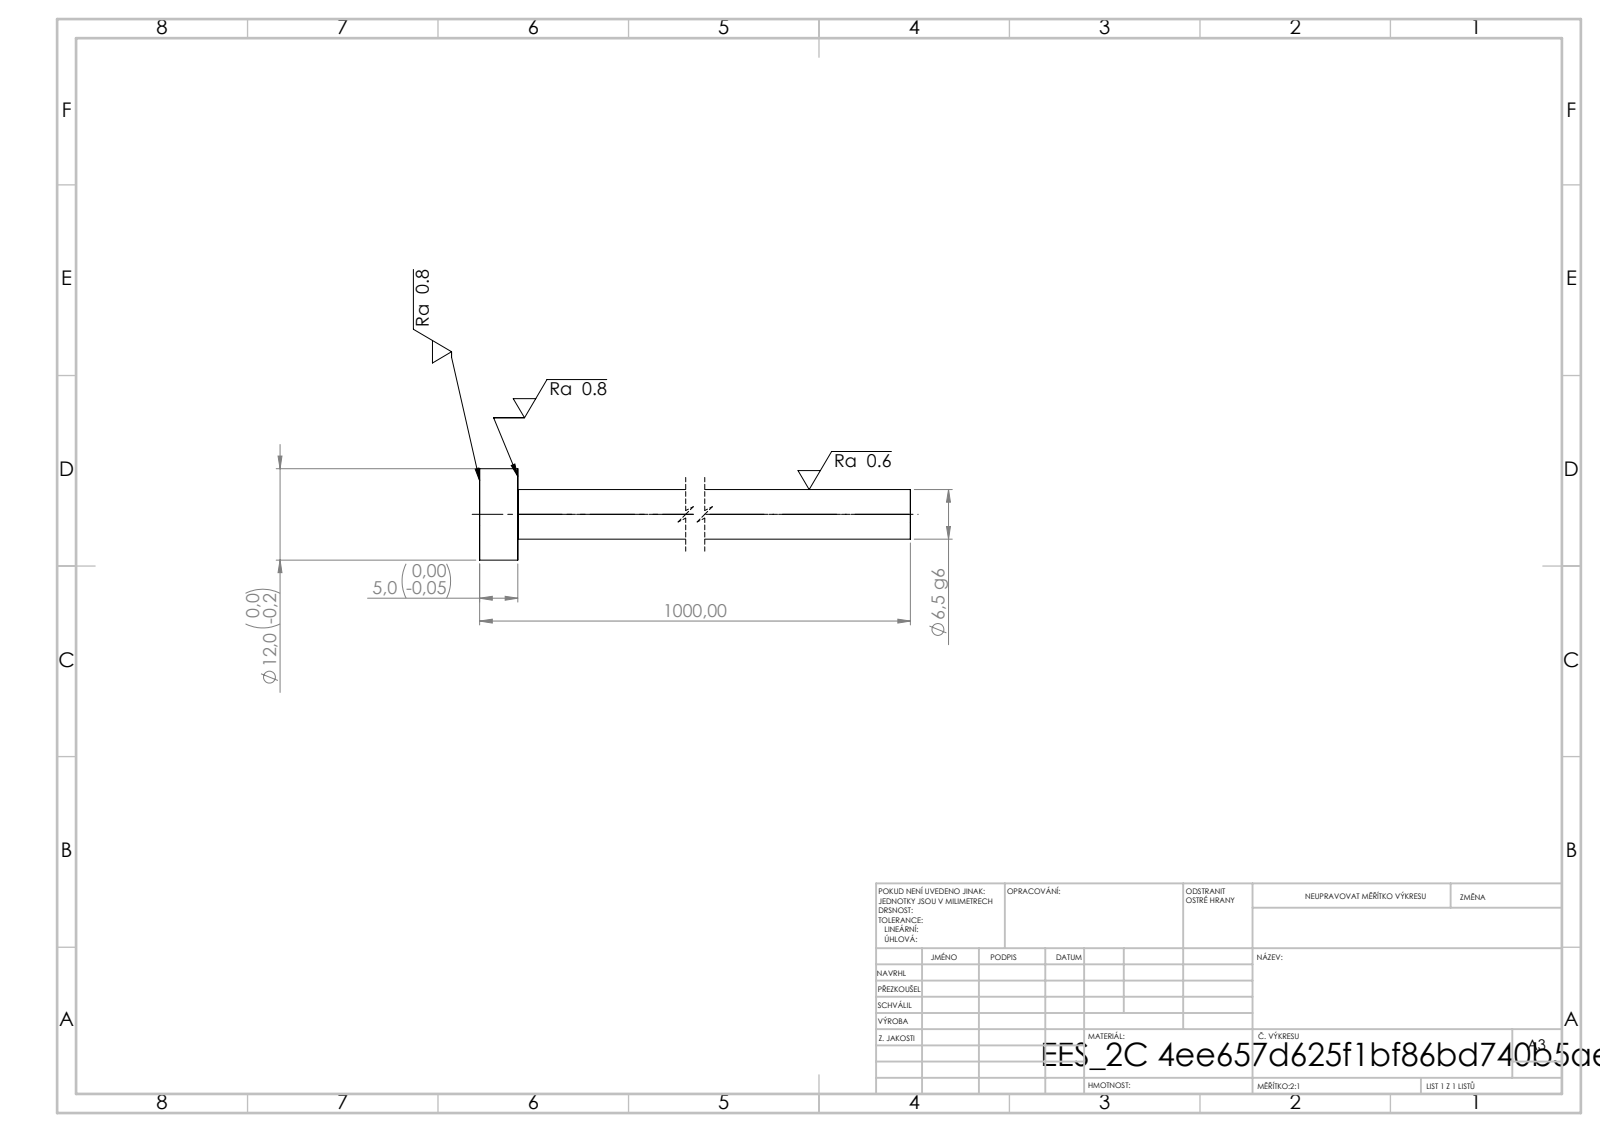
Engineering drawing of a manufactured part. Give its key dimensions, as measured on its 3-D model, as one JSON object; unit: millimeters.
{"step_written_by": "SolidWorks 2019 (CONFIG_CONTROL_DESIGN)", "units": "millimeters", "bodies": {"solids": 1, "faces": 7, "planar": 3, "cylindrical": 4, "other": 0}, "overall_size": [1000, 12, 12], "volume_mm3": 33583, "surface_area_mm2": 20733, "round_bosses_or_shafts": [[12, 1], [6.5, 1]], "face_to_face_distances": [5, 1000, 995]}
